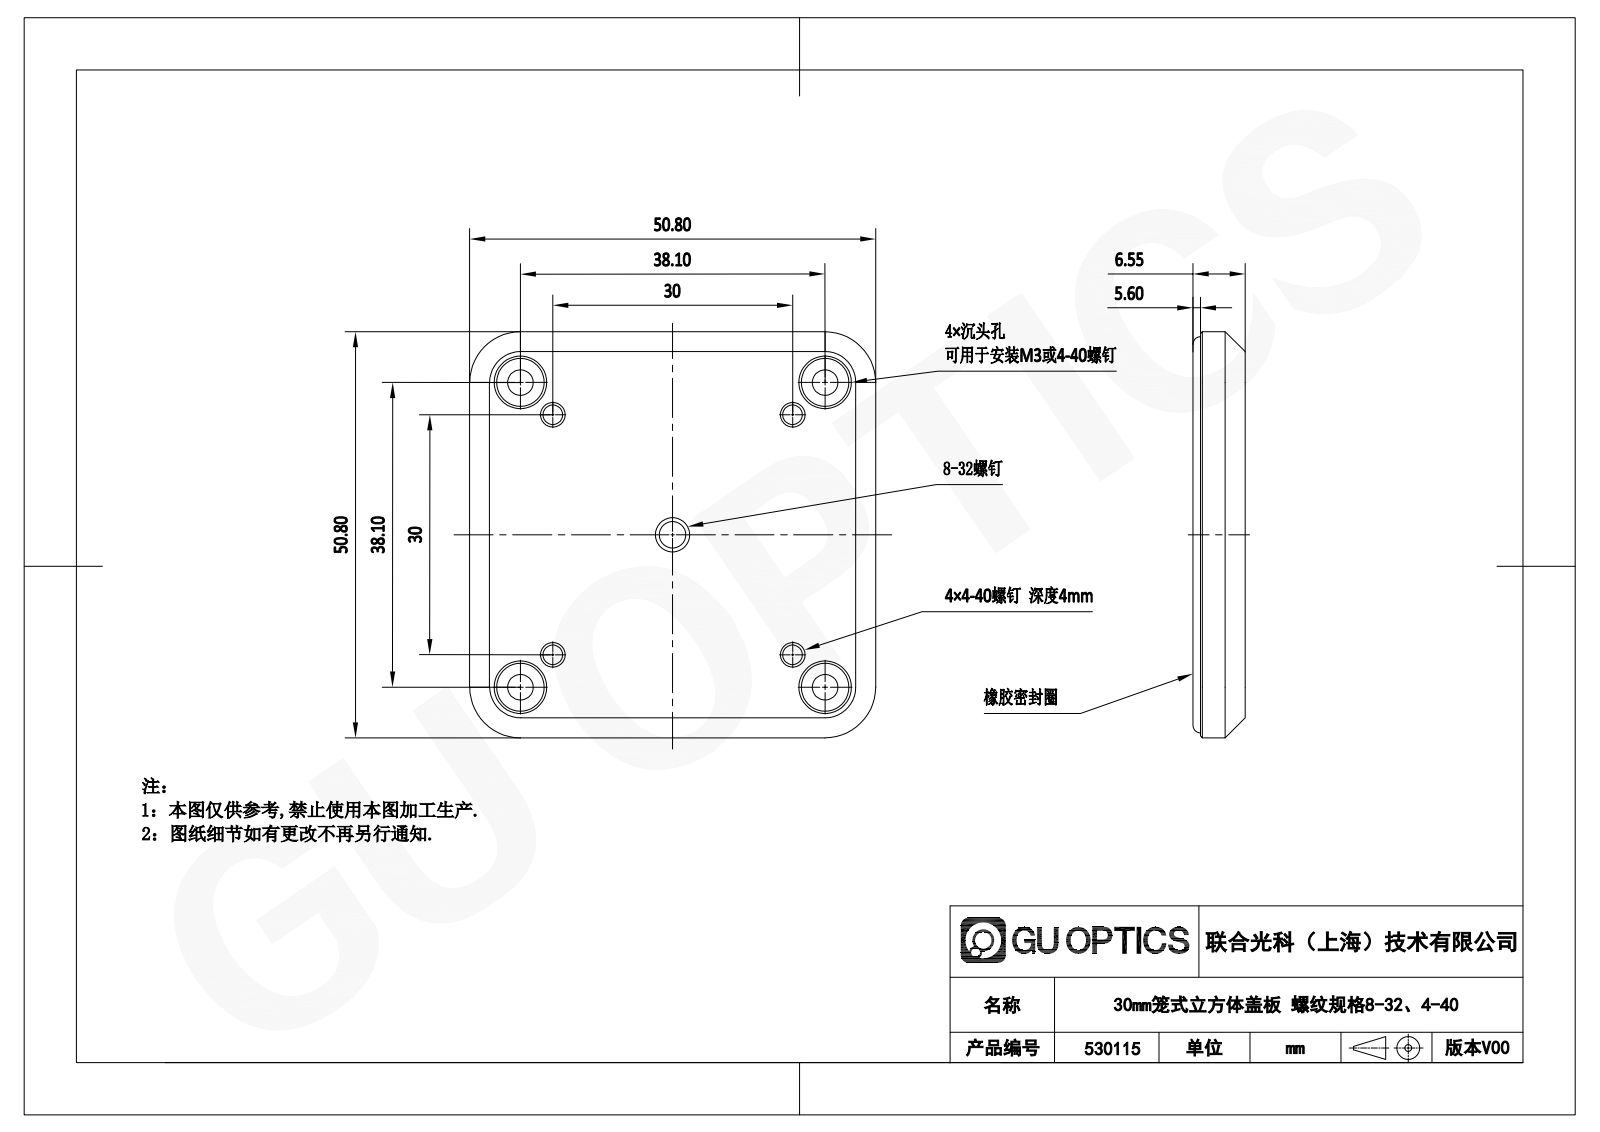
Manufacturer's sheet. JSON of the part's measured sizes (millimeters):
{"part_name": "530115", "step_written_by": "SolidWorks 2020 (CONFIG_CONTROL_DESIGN)", "units": "millimeters", "bodies": {"solids": 2, "faces": 66, "planar": 20, "cylindrical": 19, "other": 27}, "overall_size": [50.8, 50.8, 6.55], "volume_mm3": 13075, "surface_area_mm2": 7643, "round_holes": [[2.26, 4], [3.2, 4], [6, 4], [3.45, 1], [49.53, 1]], "round_bosses_or_shafts": [[45.72, 1]], "partial_cylinders_radius": [[6.35, 4]], "face_to_face_distances": [5.6, 4.08, 1.52, 50.8, 3.2, 0.88, 2.4, 37.93], "hole_center_spacings": [34.29, 5.73, 21.21, 26.94, 30, 38.1, 48.15, 42.43]}
